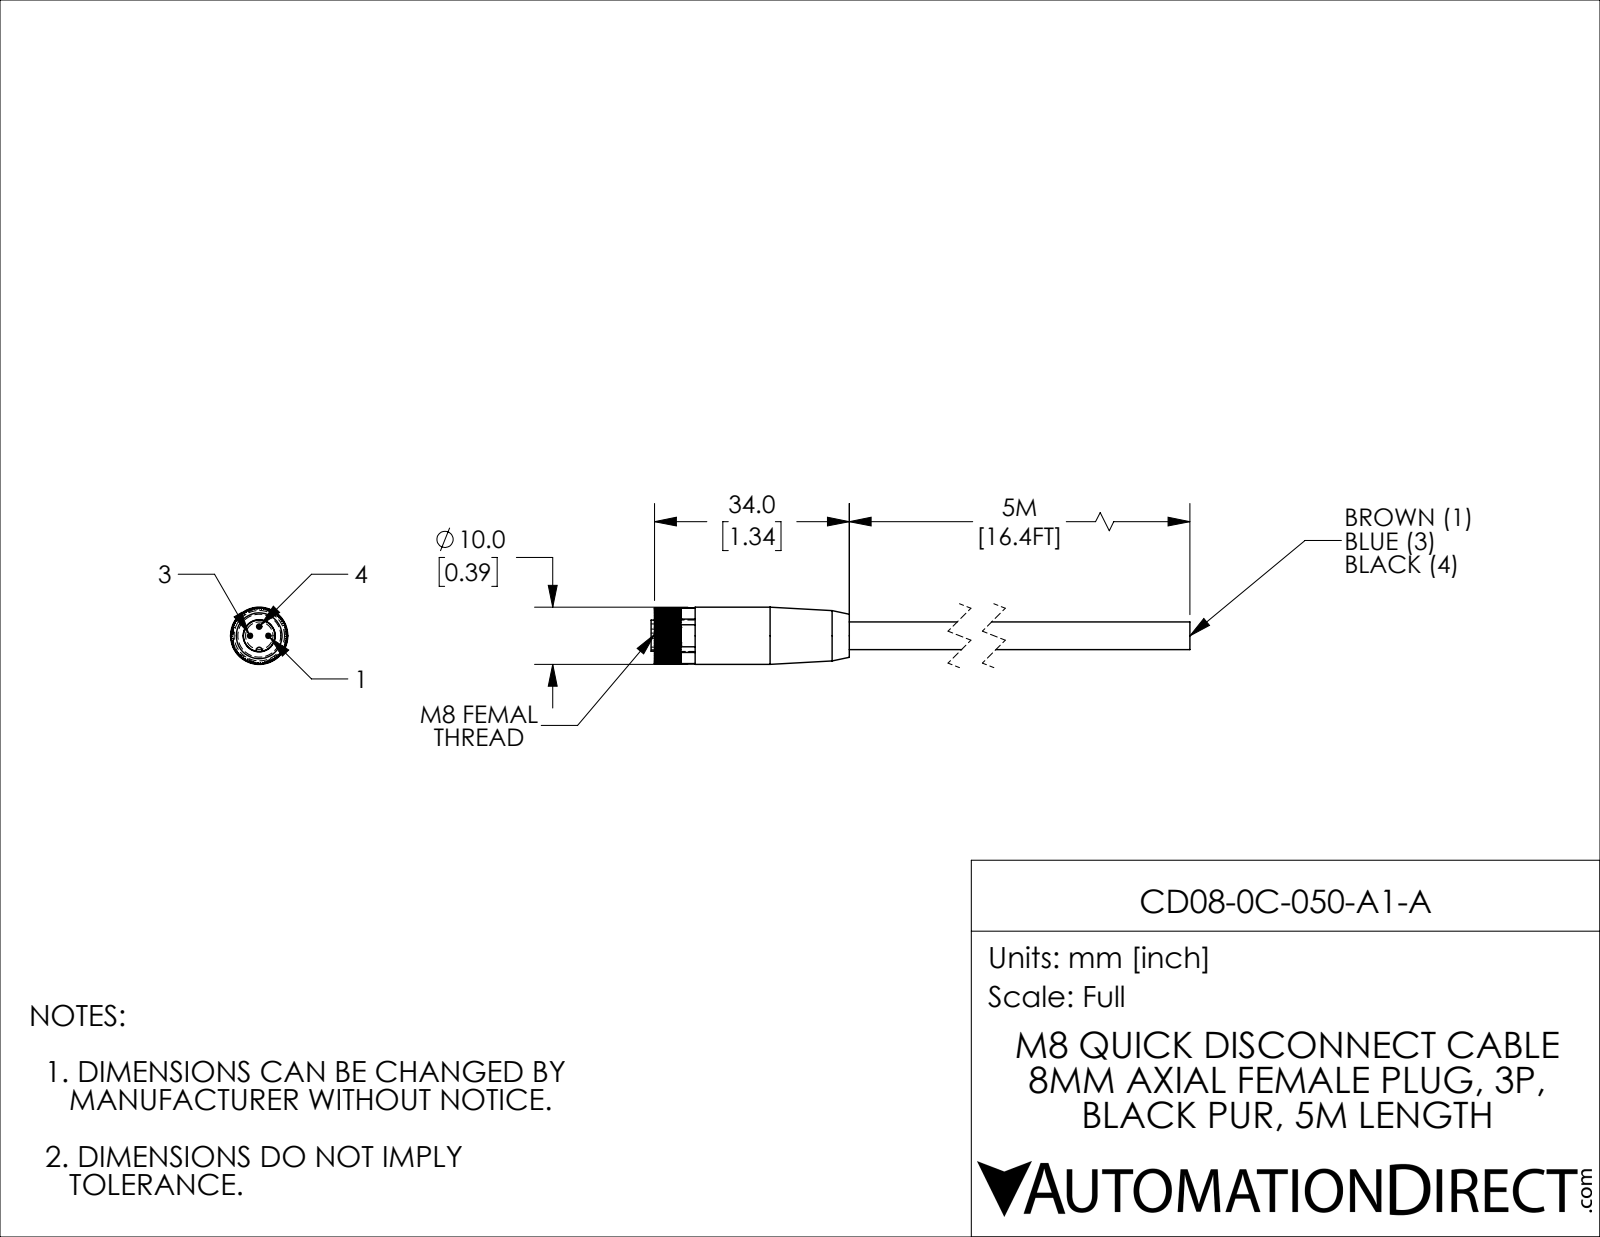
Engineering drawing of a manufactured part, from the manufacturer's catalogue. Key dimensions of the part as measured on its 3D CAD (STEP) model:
Part name (STEP PRODUCT): CD08-0C-050-A1-A
STEP written by: SolidWorks 2021 (CONFIG_CONTROL_DESIGN)
Units: inches
Bodies: 4 solids, 304 faces (222 planar, 78 cylindrical, 4 other)
Overall size (bounding box): 5.299 × 0.394 × 0.394
Volume: 0.254 in³ · Surface area: 5.036 in²
Round holes (diameter × count): ⌀0.035 ×3, ⌀0.22 ×1, ⌀0.315 ×1
Round bosses / shafts (diameter × count): ⌀0.394 ×1, ⌀0.217 ×1, ⌀0.189 ×1
Partial cylindrical surfaces — rounded edges, fillets, slot ends (radius × count): R0.02 ×1, R0.193 ×1
Main face-to-face distances: 1.059, 0.354, 0.024, 0.181, 1.181, 0.122, 0.157, 1.339, 0.28, 1.362
Hole centre spacings: 0.063, 0.089, 0.126
